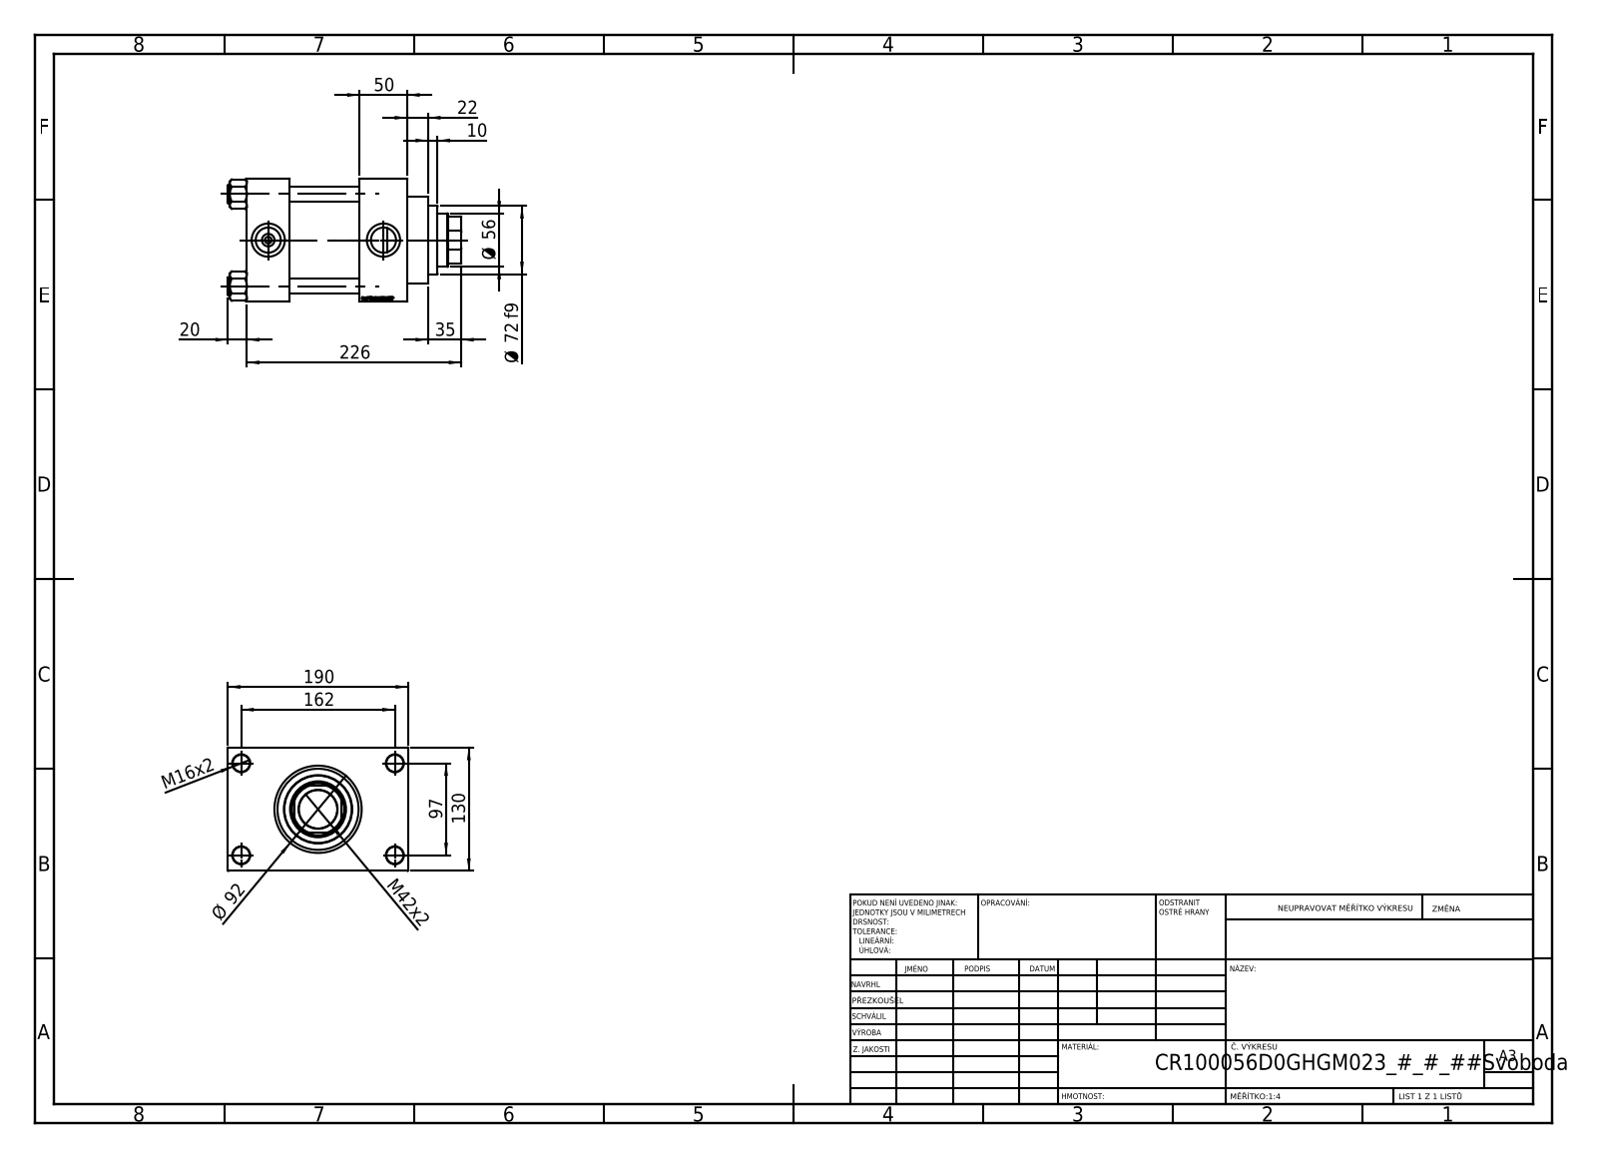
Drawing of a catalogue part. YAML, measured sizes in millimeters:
part_name: "V215CR_VCP_D; V215_VC_A; V215CR_D_TYCINKA; NUT_M5_D (+1 more)"
step_written_by: "SolidWorks 2019 (CONFIG_CONTROL_DESIGN)"
units: millimeters
bodies: {solids: 11, faces: 1151, planar: 545, cylindrical: 88, other: 518}
overall_size: [246, 190, 130]
volume: 2641000
surface_area: 365436
round_holes:
  - {diameter: 16, count: 4}
  - {diameter: 18, count: 4}
  - {diameter: 7, count: 2}
  - {diameter: 26.44, count: 2}
  - {diameter: 35, count: 2}
  - {diameter: 40.5, count: 1}
  - {diameter: 56, count: 1}
  - {diameter: 59, count: 1}
  - {diameter: 76, count: 1}
  - {diameter: 85.5, count: 1}
  - {diameter: 100, count: 1}
round_bosses_or_shafts:
  - {diameter: 19, count: 4}
  - {diameter: 106, count: 1}
  - {diameter: 92, count: 1}
  - {diameter: 72, count: 1}
partial_cylinders:
  - {radius: 27, count: 1}
face_to_face_distances: [130, 50, 45, 119, 74, 124, 169, 30, 160, 190]
hole_center_spacings: [32.55, 68.52, 94.41, 96.9, 102.27, 129.45, 161.73, 97]
